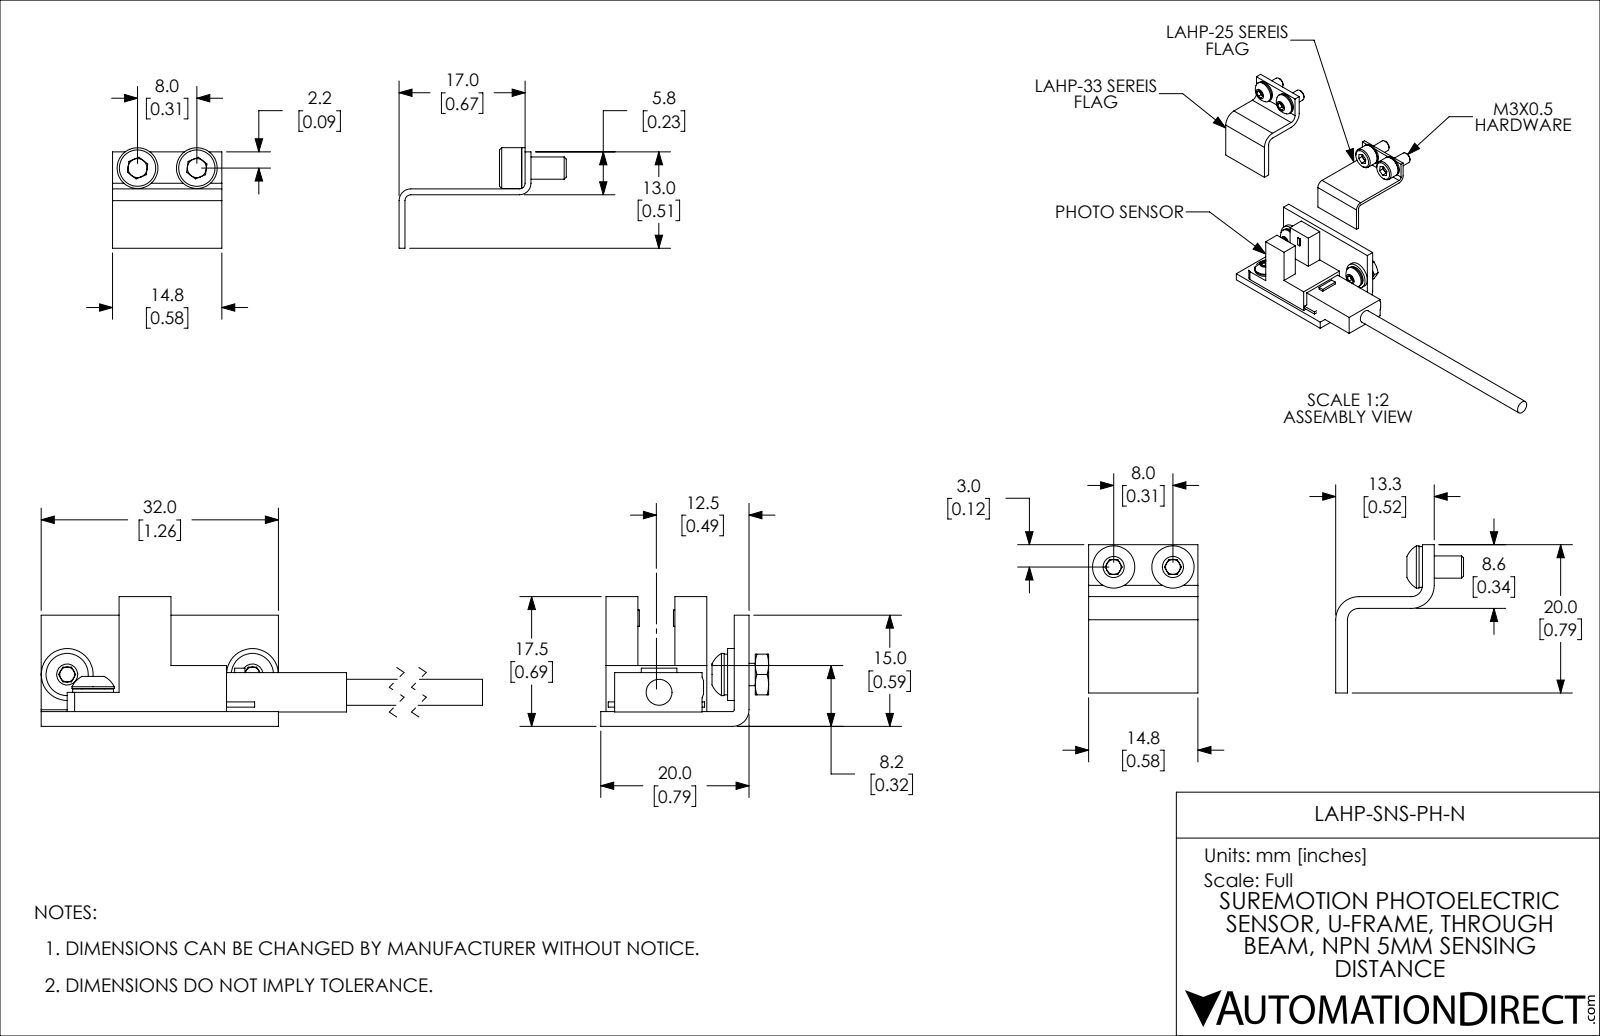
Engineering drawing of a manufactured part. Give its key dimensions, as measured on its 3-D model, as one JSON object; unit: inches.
{"part_name": "LAHP-SNS-PH-N_PHOTO SENSOR; LAHP-SNS-PH-N; LAHP-SNS-PH-N_25-FLAG; LAHP-SNS-PH-N_33-FLAG", "step_written_by": "SolidWorks 2019 (CONFIG_CONTROL_DESIGN)", "units": "inches", "bodies": {"solids": 26, "faces": 572, "planar": 276, "cylindrical": 160, "other": 136}, "overall_size": [4.407, 2.067, 1.167], "volume_in3": 0.445, "surface_area_in2": 14.42, "round_holes": [[0.126, 10], [0.102, 6], [0.039, 4], [0.098, 4], [0.134, 4], [0.118, 2], [0.138, 2], [0.145, 2]], "round_bosses_or_shafts": [[0.217, 8], [0.224, 6], [0.118, 6], [0.276, 2], [0.138, 1]], "partial_cylinders_radius": [[0.02, 8], [0.039, 2], [0.051, 2], [0.06, 2], [0.01, 1], [0.03, 1], [0.031, 1], [0.061, 1]], "face_to_face_distances": [0.079, 0.018, 0.104, 0.276, 0.237, 0.299, 0.197, 0.114, 0.394, 0.102], "hole_center_spacings": [0.315, 1.39, 0.1, 0.2, 0.276, 0.315, 0.315, 0.709]}
